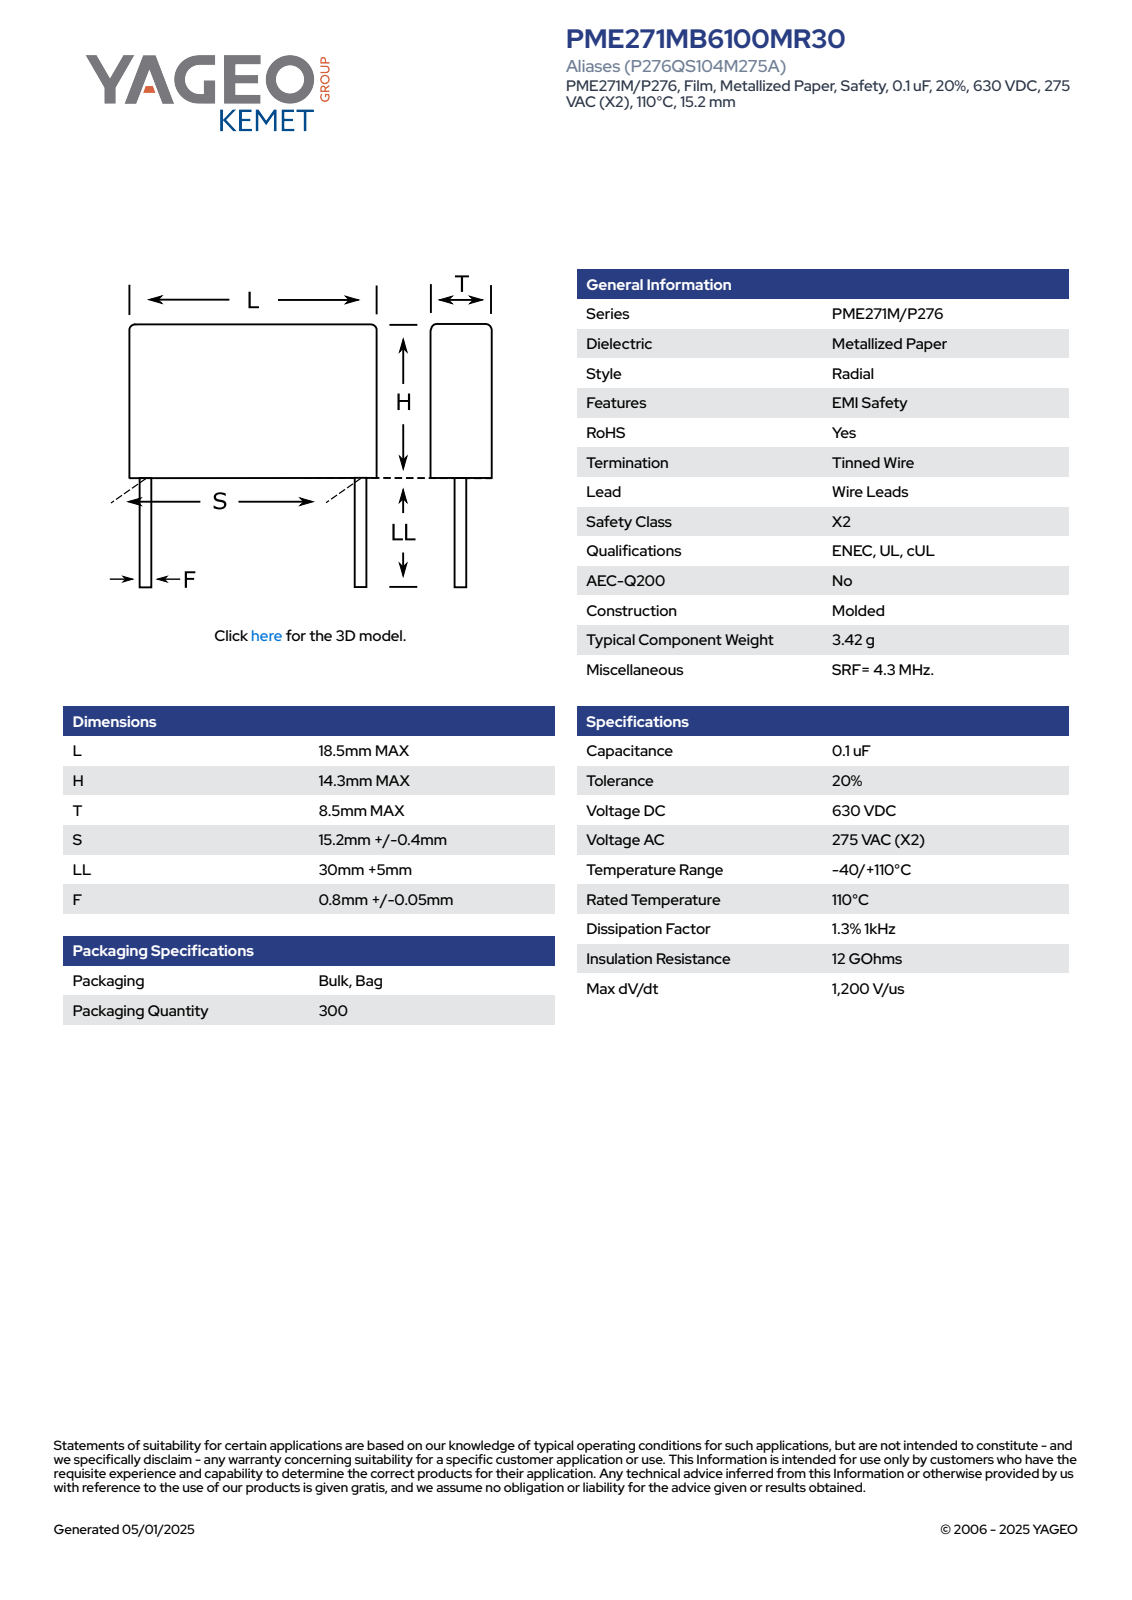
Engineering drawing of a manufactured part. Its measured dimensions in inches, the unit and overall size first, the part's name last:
Units: inches
Overall size (bounding box): 1.941 × 0.728 × 0.335
Round bosses / shafts (diameter × count): ⌀0.031 ×2
Partial cylindrical surfaces — rounded edges, fillets, slot ends (radius × count): R0.02 ×4
Main face-to-face distances: 0.335, 0.563, 0.728, 0.335, 1.378, 1.941, 1.679, 0.301, 0.262, 1.614
Volume: 0.139 in³ · Surface area: 1.964 in²
Bodies: 4 solids, 73 faces (65 planar, 8 cylindrical, 0 other)
Part name (STEP PRODUCT): CFR_MOLDED_18.5X14.3X8.5_L18.5H14.3T8.5S15.2LL35F0.8
STEP written by: SolidWorks 2014 (AUTOMOTIVE_DESIGN)
